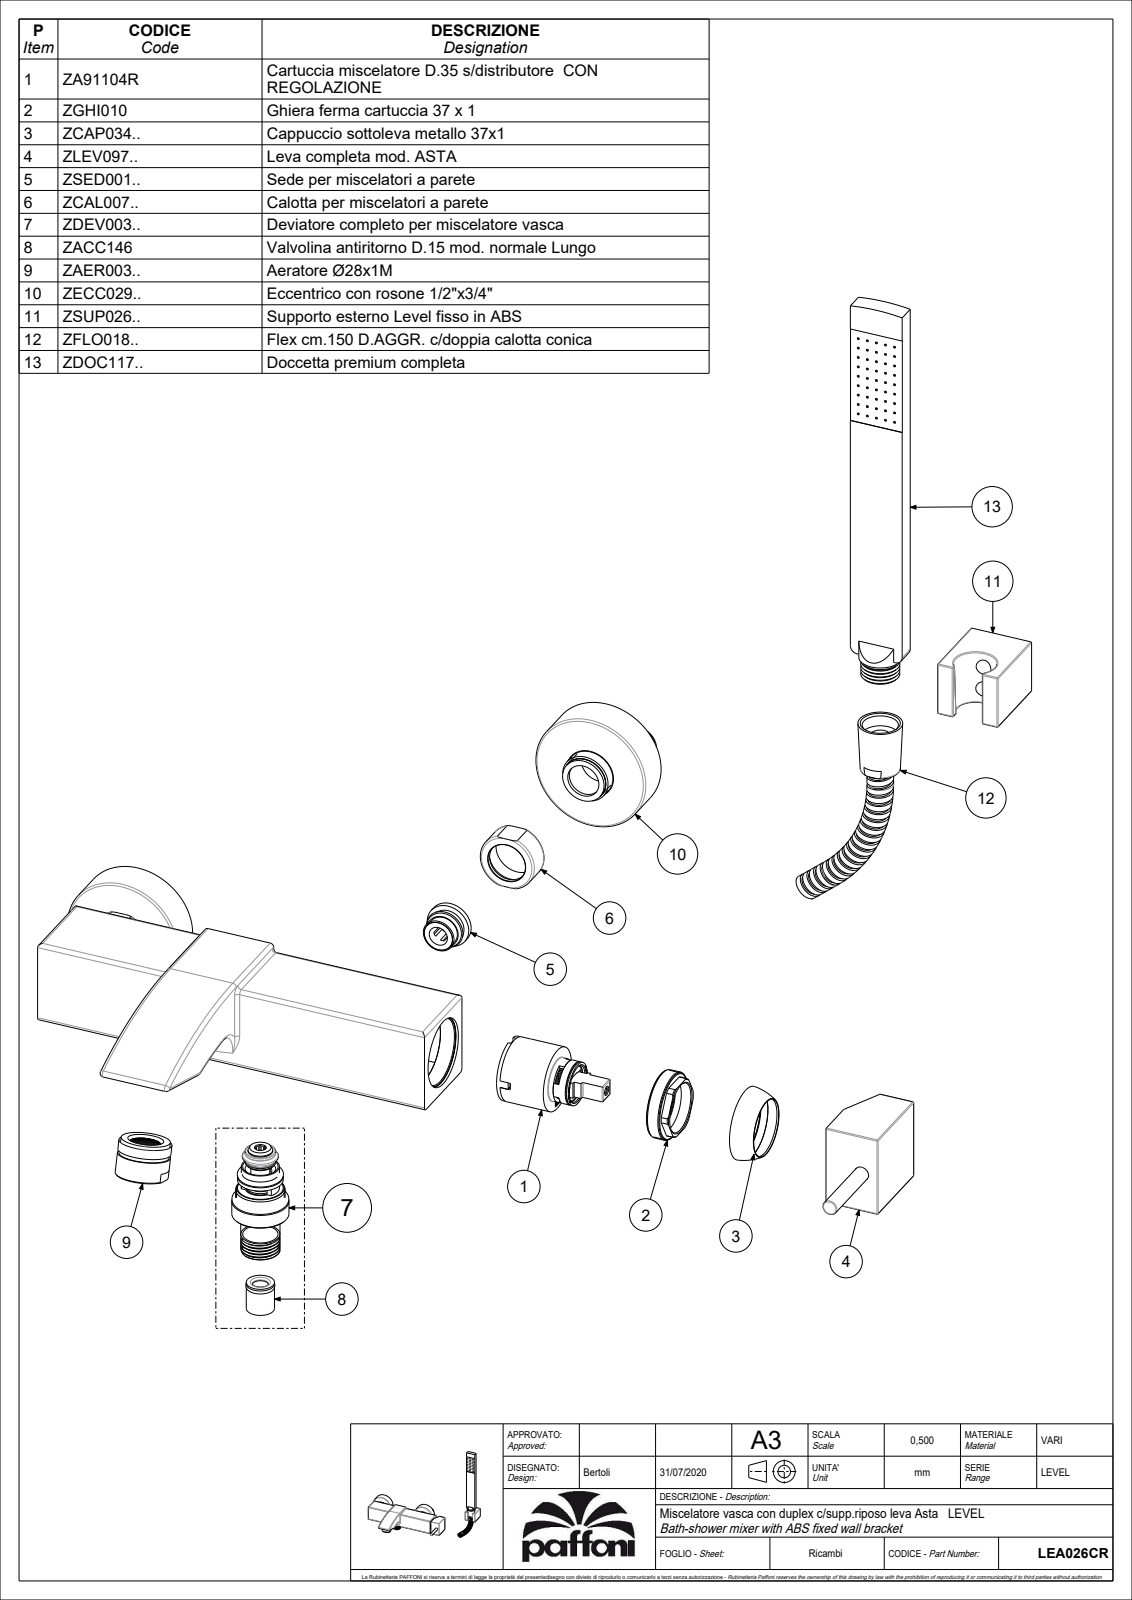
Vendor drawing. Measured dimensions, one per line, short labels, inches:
name: LEA026CR
written by: CREO PARAMETRIC BY PTC INC, 2020044 (CONFIG_CONTROL_DESIGN)
unit: in
bodies: 4 solids, 3322 faces (2534 planar, 448 cylindrical, 340 other)
size: 14.931 × 13.041 × 6.545
volume: 26.44 in³; area: 392.2 in²
holes: 4× ⌀0.276, 3× ⌀0.335, 3× ⌀0.965, 3× ⌀0.984, 2× ⌀0.157, 2× ⌀0.187, 2× ⌀0.413, 2× ⌀0.65, 2× ⌀0.709, 2× ⌀0.827, 2× ⌀0.85, 2× ⌀1.122
bosses: 11× ⌀0.079, 3× ⌀1.063, 3× ⌀0.945, 2× ⌀2.5, 2× ⌀1.102, 2× ⌀0.394, 1× ⌀1.457, 1× ⌀1.398
rounds: 51× R0.02, 15× R0.079, 11× R0.006, 4× R0.012, 2× R0.039, 2× R0.157, 2× R0.614, 1× R0.118
face distances: 0.148, 1.683, 1.831, 1.535, 0.299, 0.394, 1.982, 0.118, 2.13, 0.315
hole spacings: 0.278, 0.339, 0.449, 0.157, 0.236, 0.394, 0.512, 0.551
